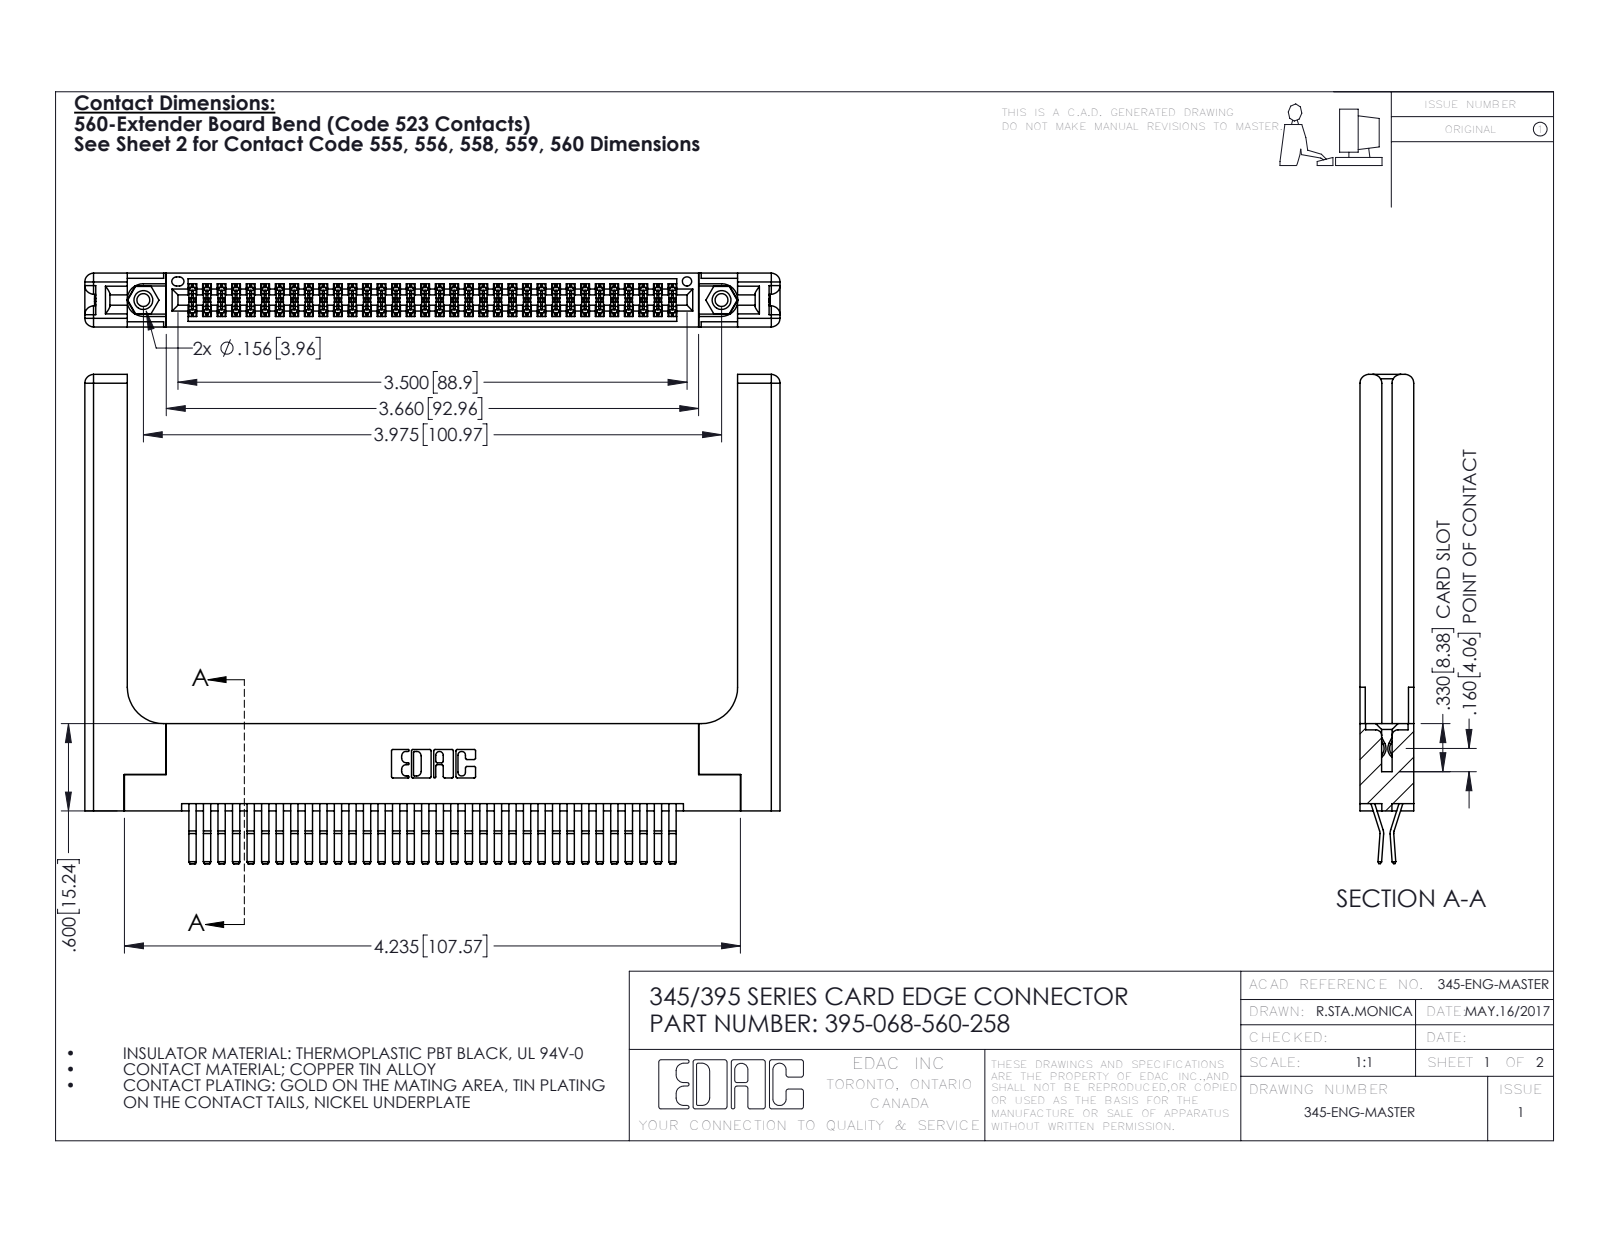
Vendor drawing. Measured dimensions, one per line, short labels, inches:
name: 345-250-001_345-250-001-102; 395-068-560-258; 345 Part_Flush Mounting Lugs - 0.156 Dia-TH; 345-292-001_560 Tail (+1 more)
written by: SolidWorks 2016 (CONFIG_CONTROL_DESIGN)
unit: in
bodies: 73 solids, 3918 faces (2472 planar, 1386 cylindrical, 60 other)
size: 4.779 × 3.362 × 0.37
volume: 1.259 in³; area: 37.25 in²
holes: 2× ⌀0.089, 2× ⌀0.125, 2× ⌀0.156, 1× ⌀0.064
bosses: 2× ⌀0.155
rounds: 102× R0.006, 22× R0.01, 16× R0.06, 6× R0.007, 6× R0.031, 3× R0.026, 2× R0.01, 2× R0.014
face distances: 0.37, 0.072, 0.298, 0.025, 0.2, 0.098, 0.272, 0.225, 0.148, 0.15
hole spacings: 0.27, 3.74, 3.975
